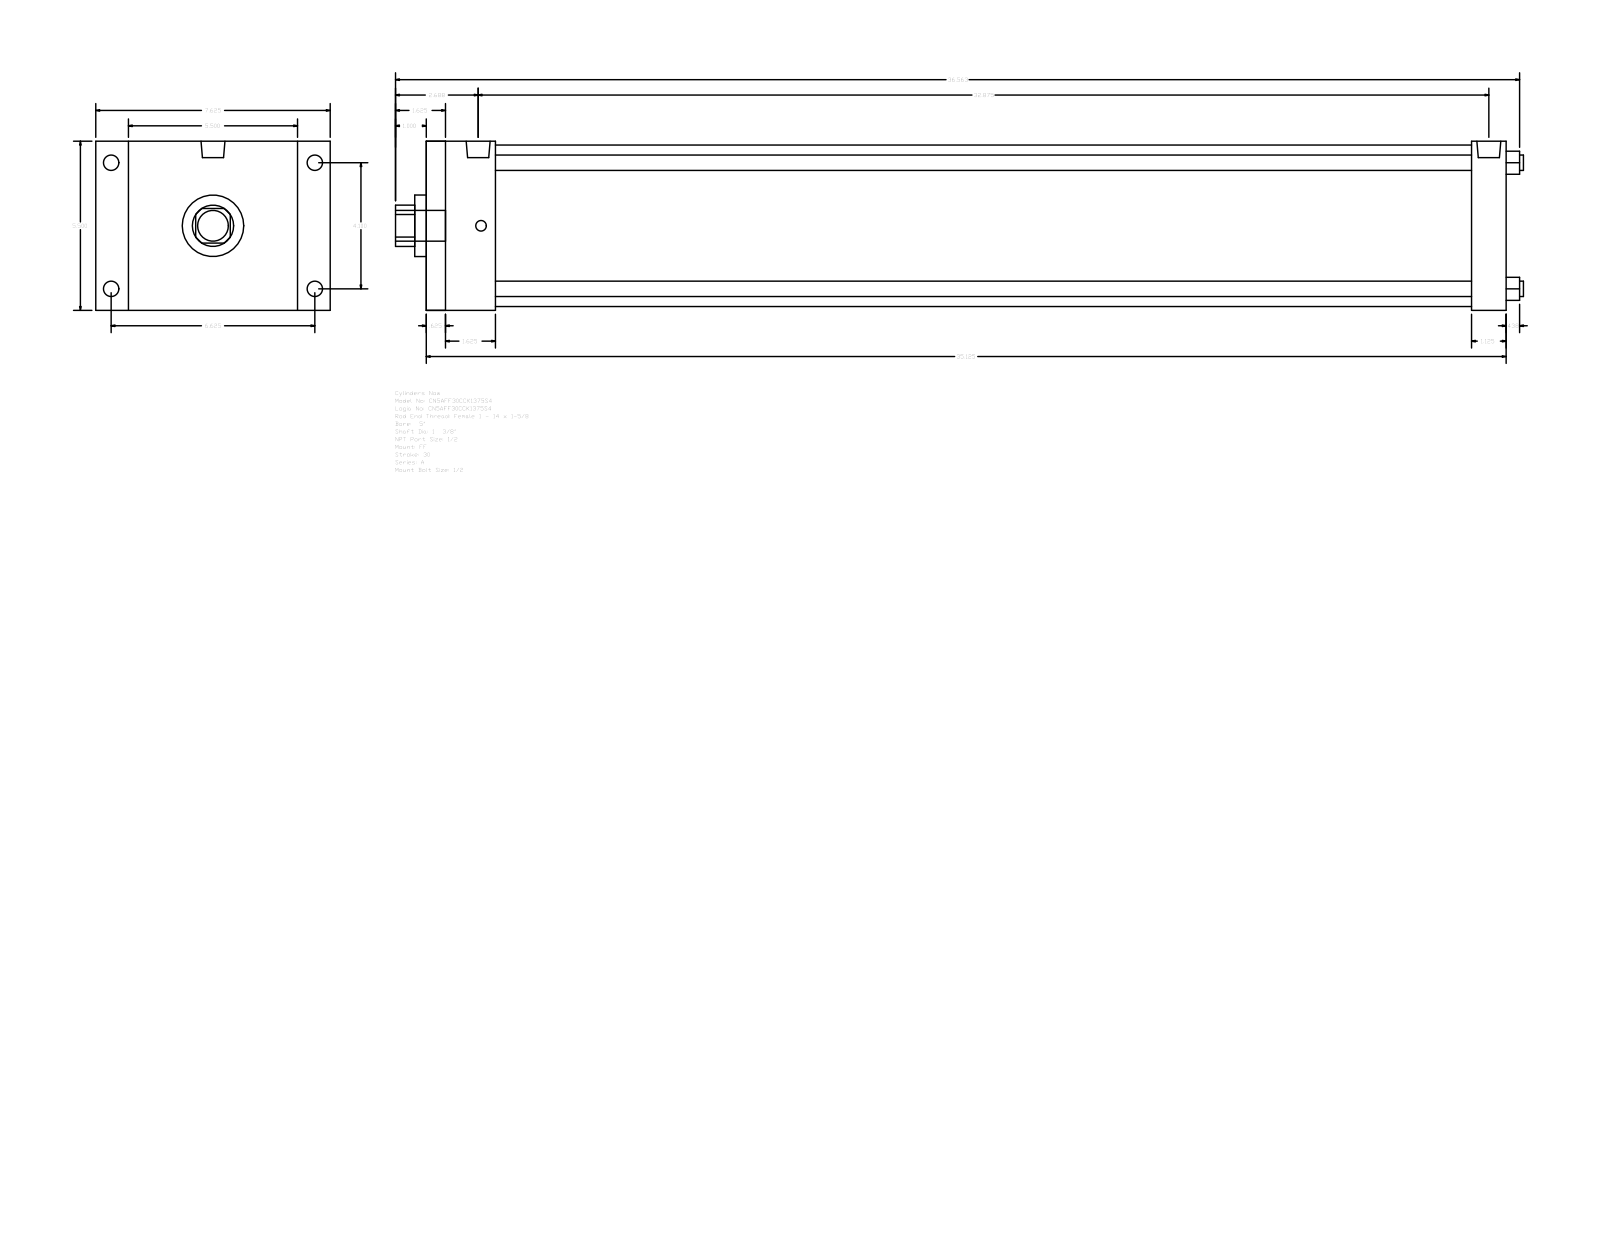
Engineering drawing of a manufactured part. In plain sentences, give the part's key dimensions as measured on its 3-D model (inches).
The part is named "A_FF__0500_1.375". Its 3-D file was written by "GSSL Pune (CONFIG_CONTROL_DESIGN)". It is 0 solids with 92 faces: 64 planar, 28 cylindrical and 0 other. Overall it measures 36.687 by 7.625 by 5.5 inches. Round holes: 4 of diameter 0.5, 1 of diameter 1.375, 1 of diameter 2, 1 of diameter 5.25. Round bosses or shafts: 4 of diameter 0.5, 4 of diameter 0.344, 2 of diameter 0.778, 1 of diameter 1. Partial cylindrical surfaces (rounded edges, fillets, slot ends): 1 of radius 0.672. The main face-to-face distances are 5.5, 35.125, 0.625, 34.5, 1.125, 34, 33.375, 2.25, 1.625, 31.75. The hole center spacings are 2.899, 4.1, 5.798.
